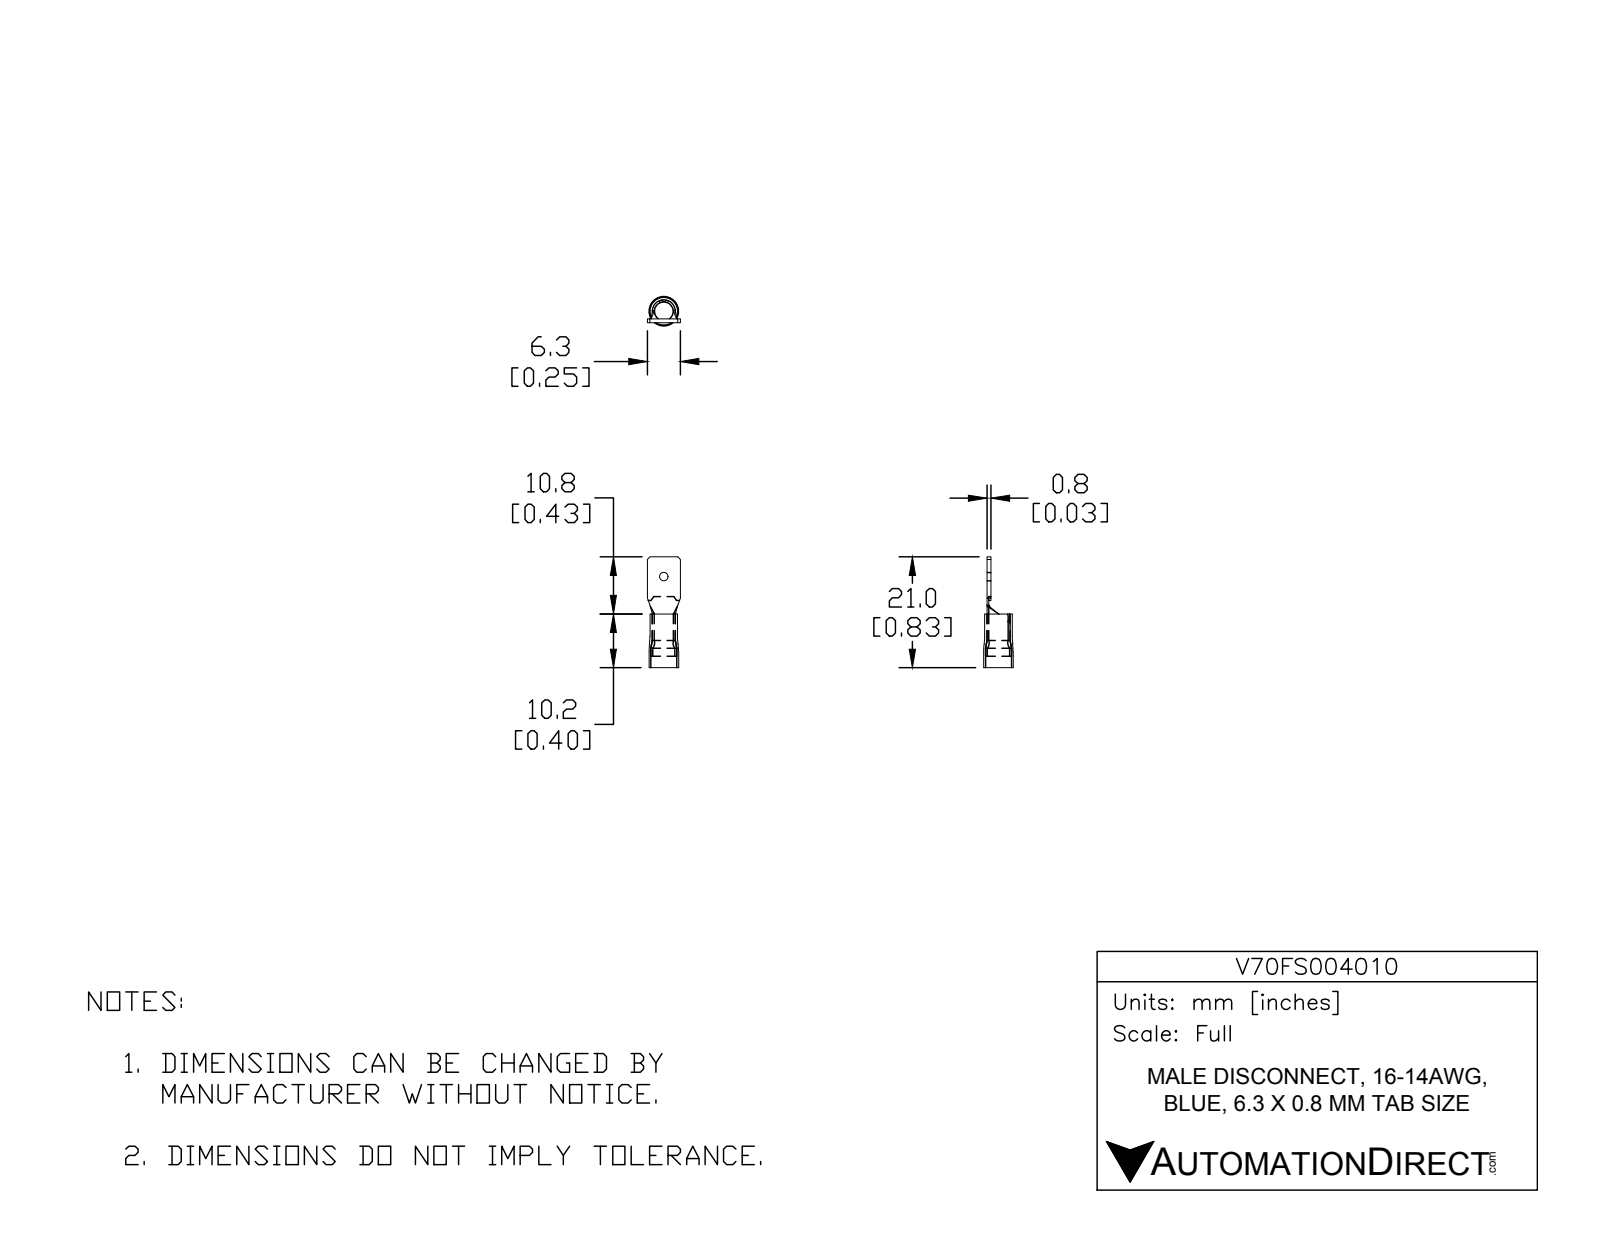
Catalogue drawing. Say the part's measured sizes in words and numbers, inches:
The part is named "V70FS004010". Its 3-D file was written by "SolidWorks 2017 (AUTOMOTIVE_DESIGN)". It is 2 solids with 66 faces: 22 planar, 22 cylindrical and 22 other. Overall it measures 0.826 by 0.246 by 0.22 inches. Its volume is 0.009 cubic inches and its surface area 1.09 square inches. Round holes: 1 of diameter 0.063, 1 of diameter 0.144, 1 of diameter 0.165, 1 of diameter 0.171, 1 of diameter 0.193. Round bosses or shafts: 1 of diameter 0.22, 1 of diameter 0.205. Partial cylindrical surfaces (rounded edges, fillets, slot ends): 4 of radius 0.02. The main face-to-face distances are 0.03, 0.016, 0.014, 0.401, 0.246, 0.086, 0.315, 0.826, 0.74, 0.425.
